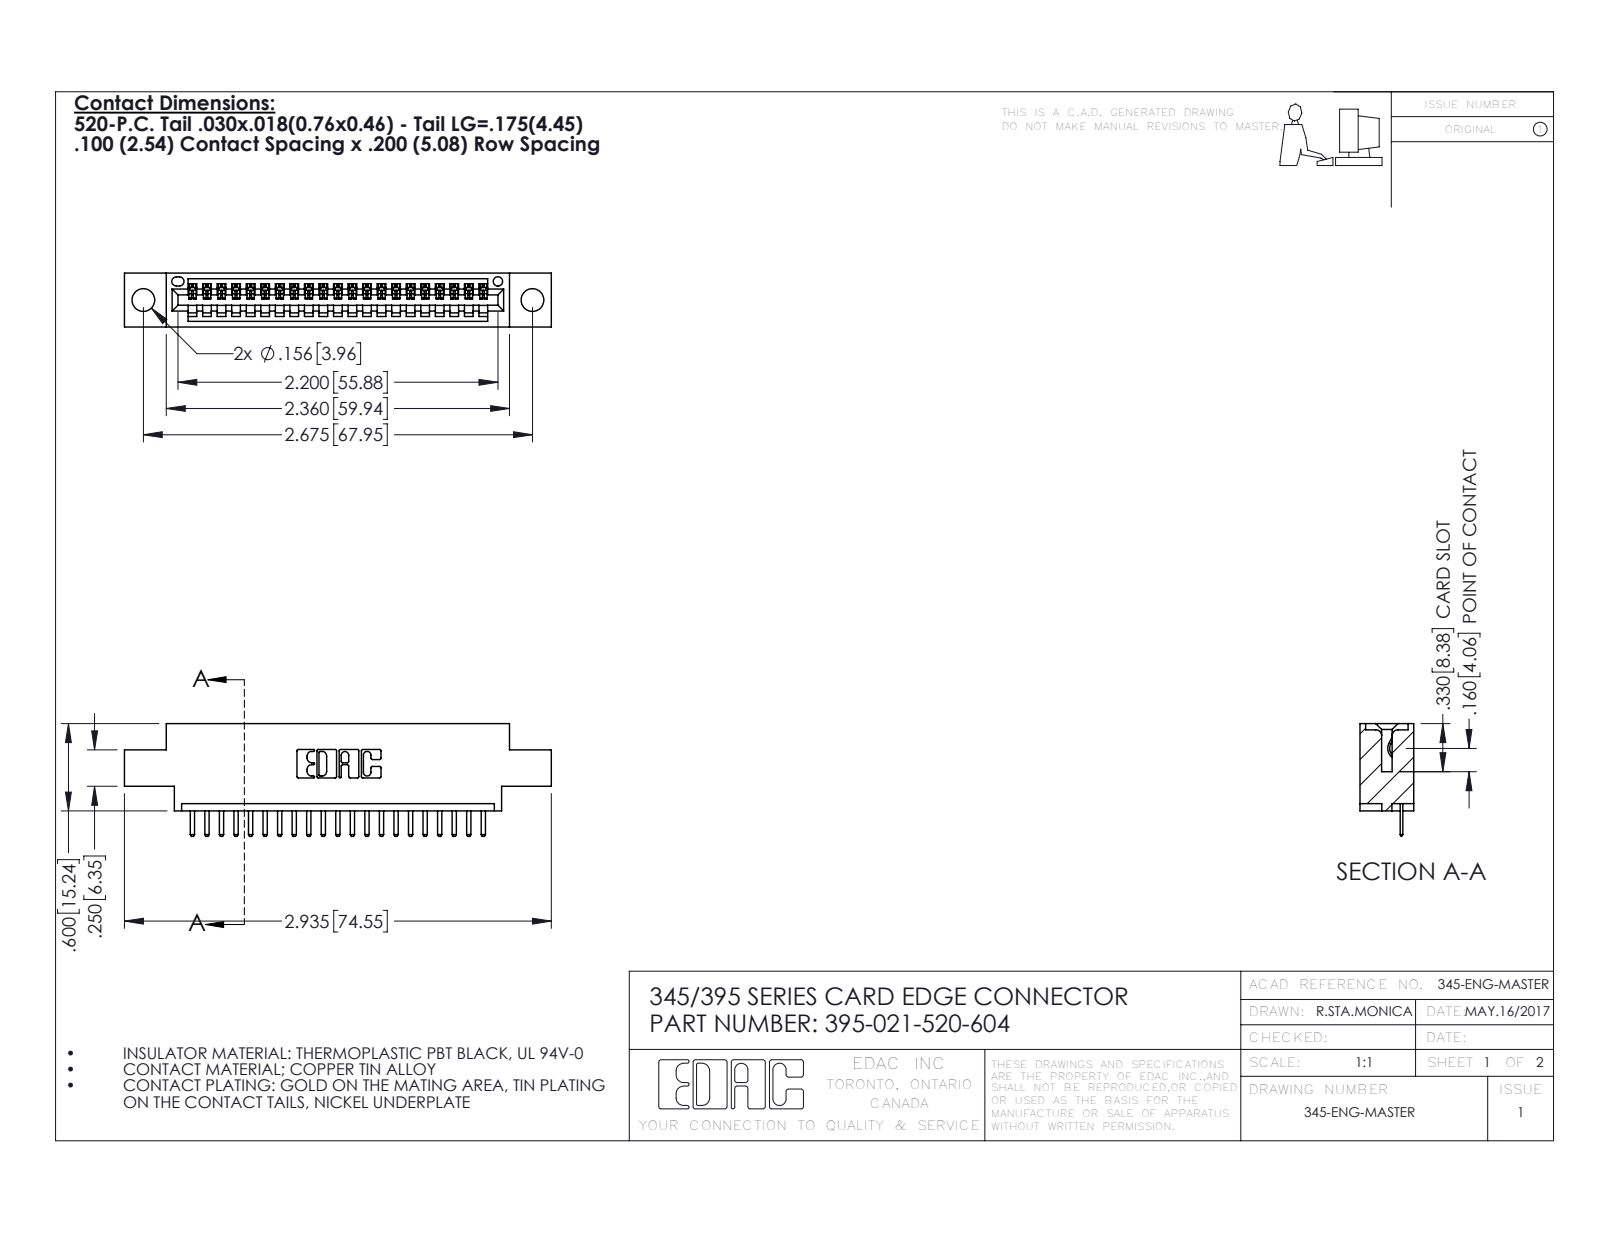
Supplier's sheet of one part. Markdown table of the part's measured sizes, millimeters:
| quantity | value |
| --- | --- |
| part name | 395-021-520-604; 345 Part_0.170 Offset - 0.156 Dia-TH; 345-292-001_345-293-120 |
| STEP written by | SolidWorks 2016 (CONFIG_CONTROL_DESIGN) |
| units | millimeters |
| bodies | 22 solids, 1432 faces (966 planar, 466 cylindrical, 0 other) |
| overall size | 74.5 × 19.7 × 9.4 |
| volume | 6 650 mm³ |
| surface area | 8 284 mm² |
| round holes (diameter × count) | 4 × 2, 1.6 × 1 |
| partial cylindrical surfaces (radius × count) | 0.3 × 44, 0.2 × 42, 0.3 × 22, 0.2 × 6, 0.8 × 6, 0.7 × 3, 0.8 × 2, 1 × 2 |
| main face-to-face distances | 9.4, 7.6, 1.8, 5.1, 2.5, 6.9, 0.6, 5.7, 1.8, 4.4 |
| hole center spacings | 6.9, 62, 67.9 |
